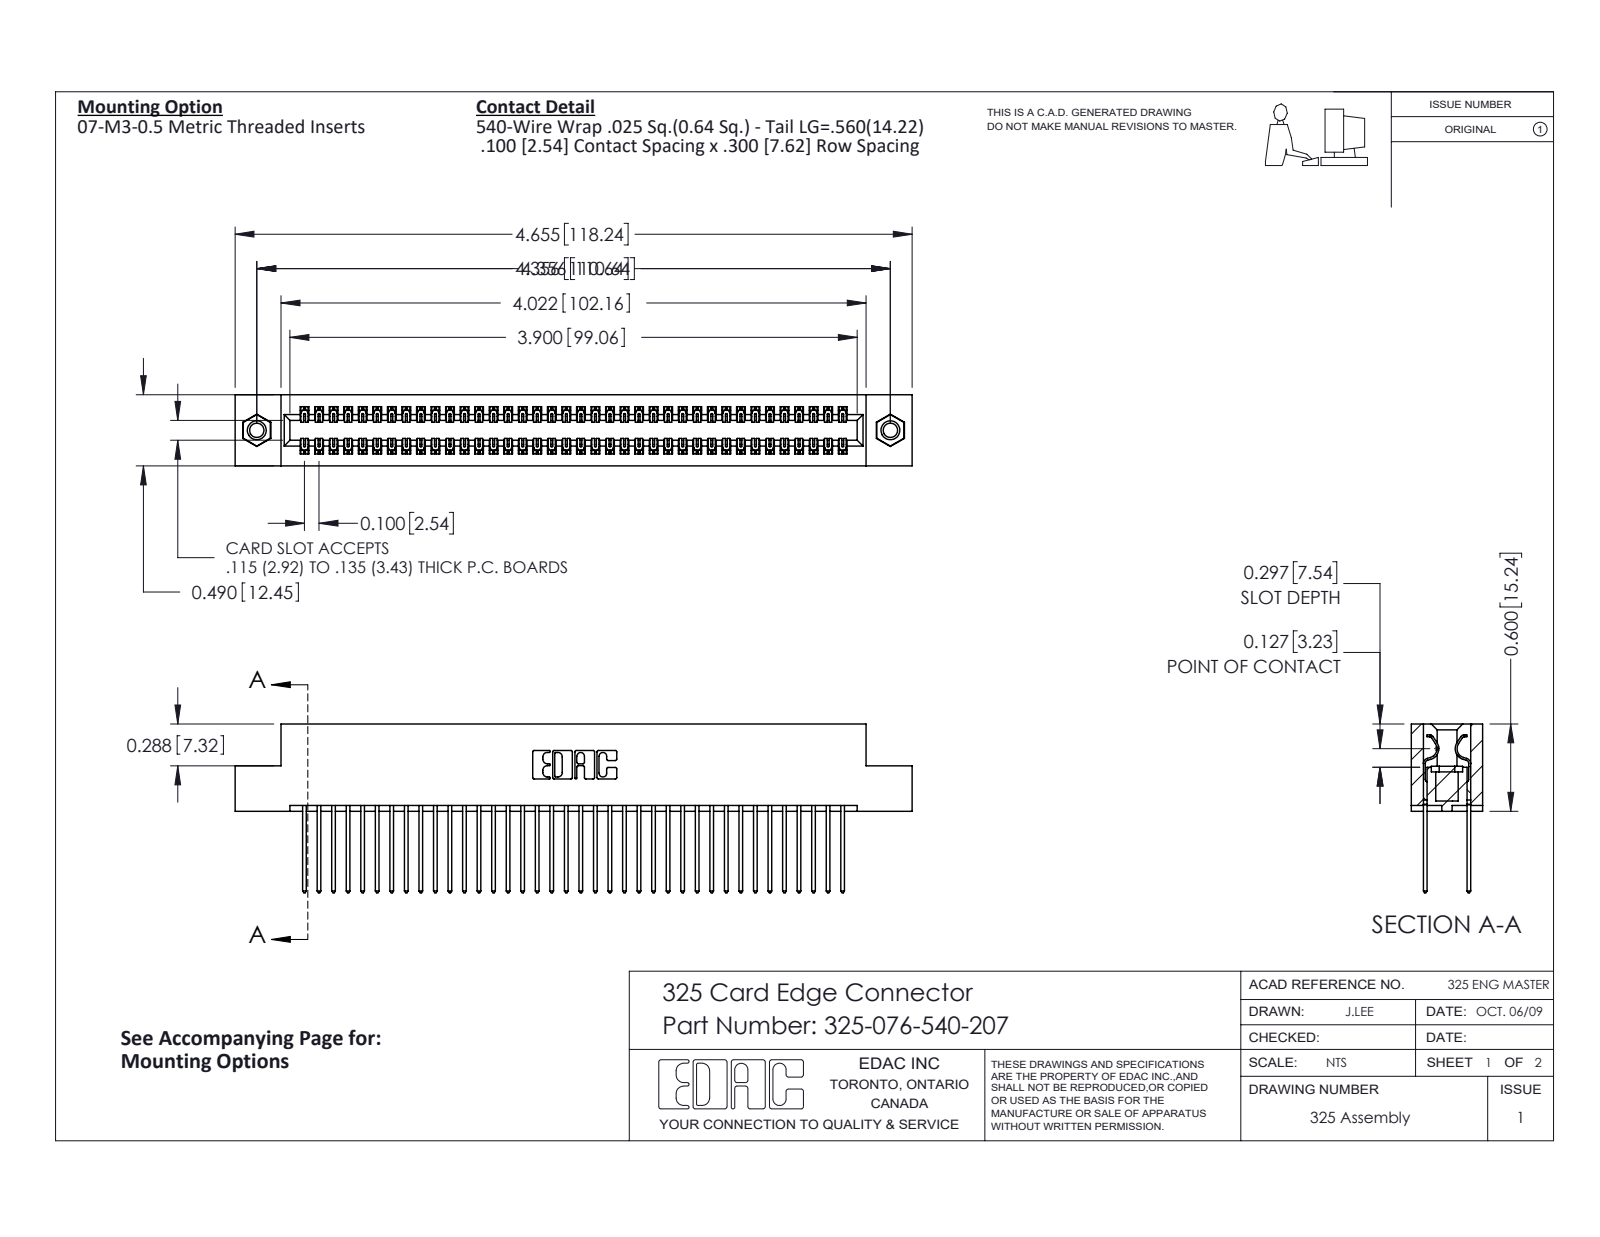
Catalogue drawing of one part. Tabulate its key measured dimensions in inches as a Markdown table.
| quantity | value |
| --- | --- |
| part name | 325-292-001_325-293-140; 325 Part_TI; 345-250-001_345-250-005-103; 325-076-540-207 |
| STEP written by | SolidWorks 2016 (CONFIG_CONTROL_DESIGN) |
| units | inches |
| bodies | 79 solids, 4126 faces (2838 planar, 1272 cylindrical, 16 other) |
| overall size | 4.655 × 1.16 × 0.49 |
| volume | 0.946 in³ |
| surface area | 31.1 in² |
| round holes (diameter × count) | 0.098 × 2, 0.125 × 2, 0.16 × 2 |
| round bosses / shafts (diameter × count) | 0.155 × 2 |
| partial cylindrical surfaces (radius × count) | 0.006 × 114, 0.01 × 76, 0.01 × 22, 0.007 × 6, 0.031 × 6, 0.026 × 3, 0.014 × 2, 0.022 × 2 |
| main face-to-face distances | 0.083, 0.407, 0.3, 0.107, 0.383, 0.025, 0.49, 0.325, 0.275, 0.56 |
| hole center spacings | 4.356 |
